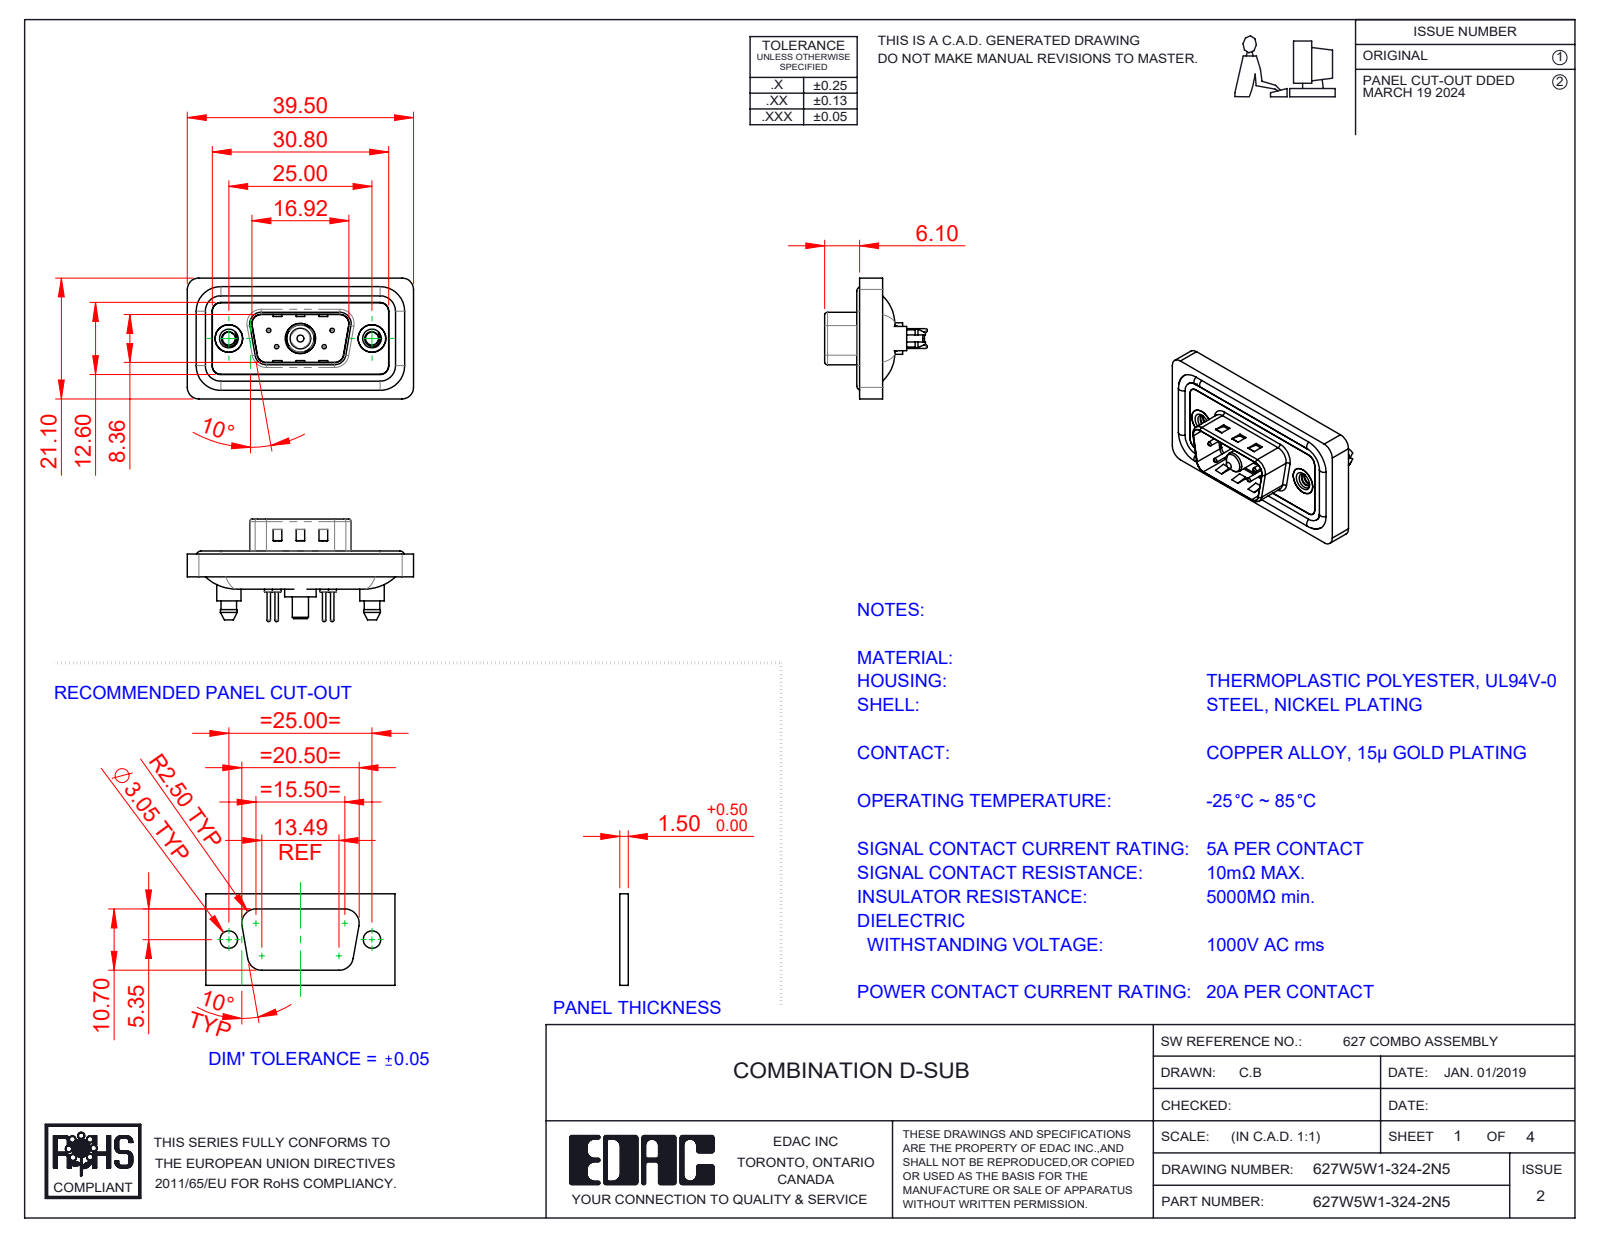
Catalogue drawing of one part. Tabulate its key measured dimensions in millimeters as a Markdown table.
| quantity | value |
| --- | --- |
| part name | 627Combo Threaded Boardlock_5; 627Combo Contact Row 2_24; 627W5W1-324-2N5; 627Combo Shell Front_09 Contacts (+5 more) |
| STEP written by | SolidWorks 2023 (CONFIG_CONTROL_DESIGN) |
| units | millimeters |
| bodies | 13 solids, 648 faces (199 planar, 287 cylindrical, 162 other) |
| overall size | 39.5 × 21.1 × 17.9 |
| volume | 4 521 mm³ |
| surface area | 7 274 mm² |
| round holes (diameter × count) | 0.75 × 4, 1.6 × 4, 2 × 4, 2.26 × 2, 4 × 2, 4.8 × 2, 5 × 2, 4.85 × 1, 5.3 × 1 |
| round bosses / shafts (diameter × count) | 1.6 × 4, 1.5 × 4, 0.6 × 4, 5.4 × 2, 4.9 × 2, 4.25 × 2, 5.5 × 1, 5.2 × 1 |
| partial cylindrical surfaces (radius × count) | 1.5 × 24, 2 × 18, 1.6 × 10, 0.5 × 8, 0.25 × 4, 0.6 × 4, 0.65 × 4, 0.9 × 4 |
| main face-to-face distances | 0.4, 1.1, 2.9, 1.6, 1.5, 3.1, 0.5, 2.5, 4, 0.8 |
| hole center spacings | 3.16, 5.72, 7.1, 12.5, 18.1, 4.39, 4.4, 8.31 |
